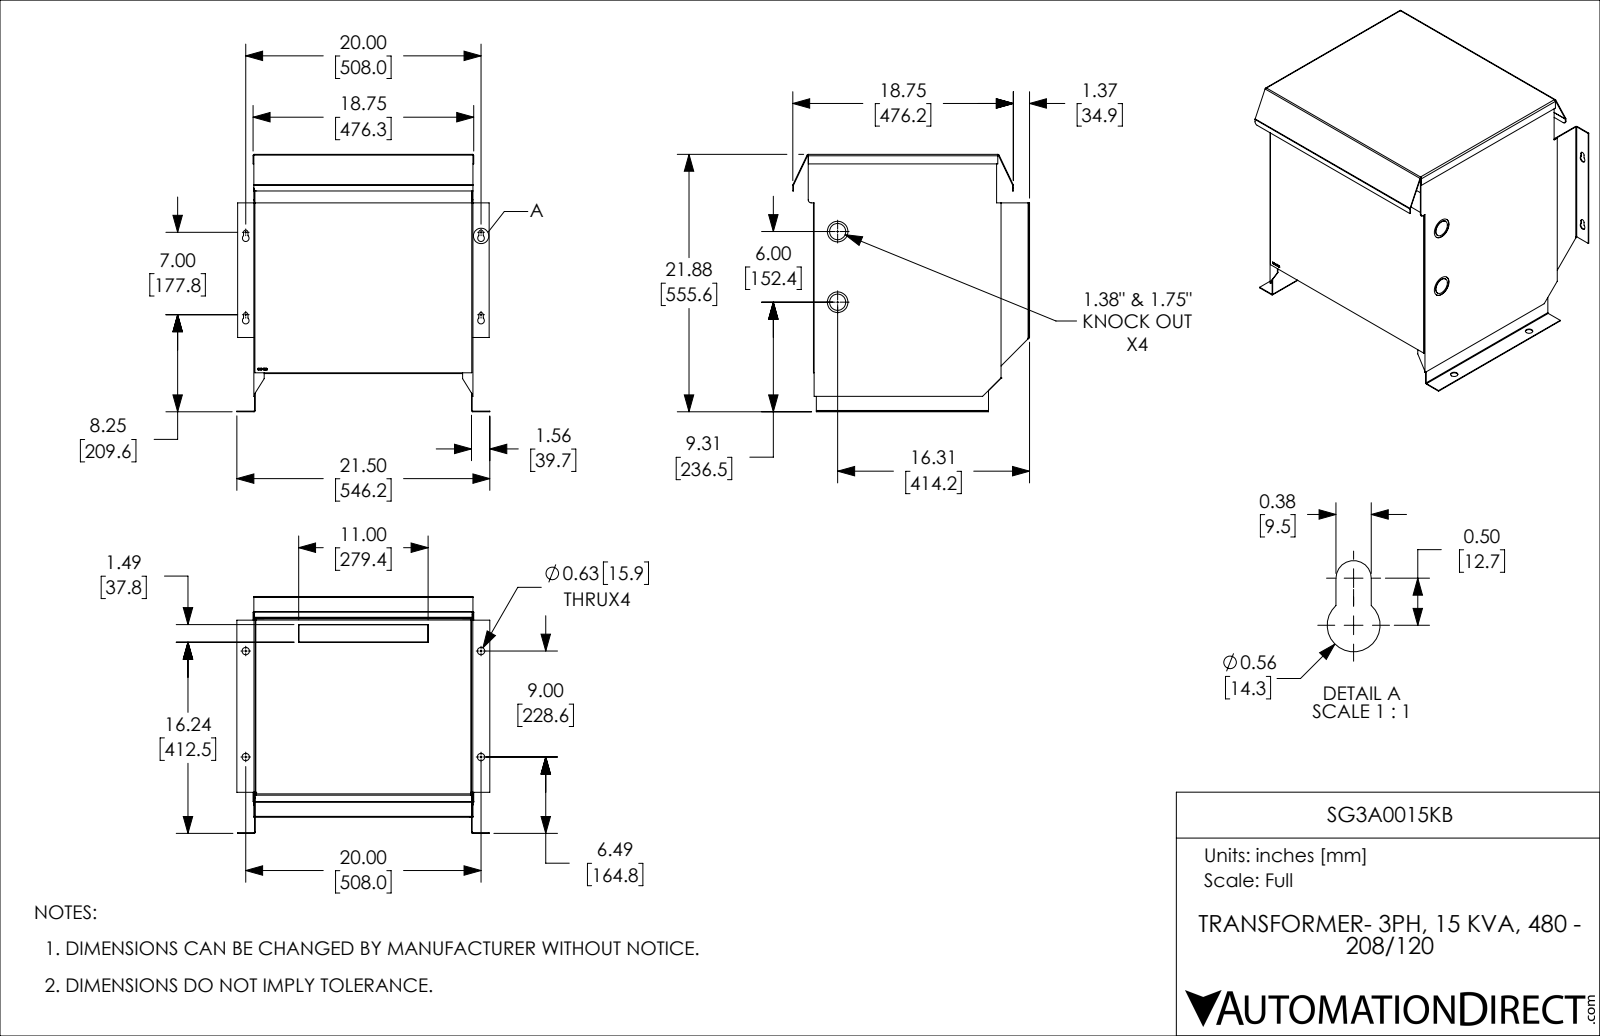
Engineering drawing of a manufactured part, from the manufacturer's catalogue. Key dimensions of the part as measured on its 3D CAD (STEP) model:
Part name (STEP PRODUCT): SG3A0015KB
STEP written by: SolidWorks 2018 (AUTOMOTIVE_DESIGN)
Units: inches
Bodies: 7 solids, 313 faces (205 planar, 80 cylindrical, 28 other)
Overall size (bounding box): 21.875 × 21.502 × 20.121
Volume: 140.5 in³ · Surface area: 4 721 in²
Round holes (diameter × count): ⌀0.625 ×3, ⌀1.75 ×2, ⌀0.625 ×1
Round bosses / shafts (diameter × count): ⌀1.375 ×2
Partial cylindrical surfaces — rounded edges, fillets, slot ends (radius × count): R0.05 ×12, R0.112 ×7, R0.06 ×6, R0.113 ×5, R0.122 ×5, R0.188 ×4, R0.281 ×4, R0.25 ×3
Main face-to-face distances: 0.063, 0.06, 18.561, 18.563, 18.501, 0.05, 18.5, 18.621, 18.625, 15.057
Hole centre spacings: 9, 20, 21.932, 6
